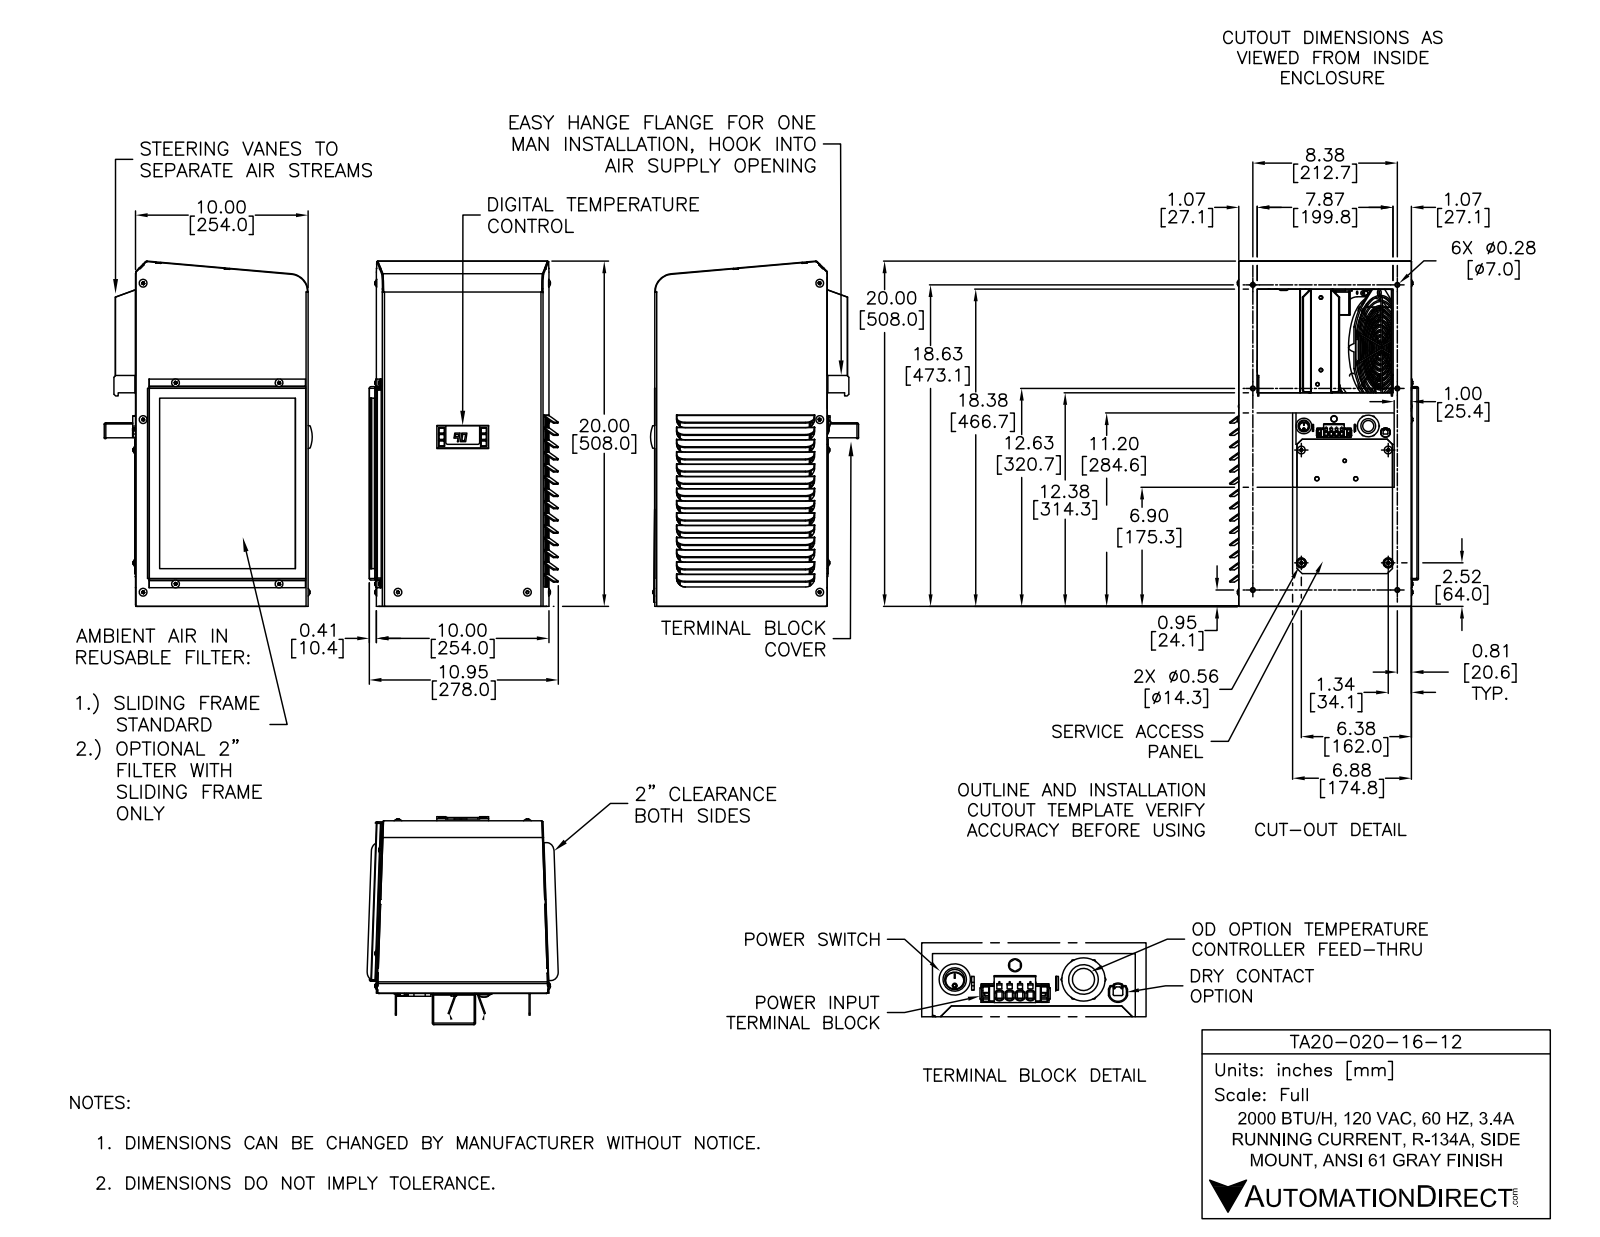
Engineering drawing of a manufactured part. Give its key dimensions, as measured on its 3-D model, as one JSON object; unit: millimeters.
{"part_name": "TA20-020-16-12", "step_written_by": "SolidWorks 2019 (AUTOMOTIVE_DESIGN)", "units": "millimeters", "bodies": {"solids": 52, "faces": 2157, "planar": 1121, "cylindrical": 737, "other": 299}, "overall_size": [508, 288.1, 279.5], "volume_mm3": 6576000, "surface_area_mm2": 1777000, "round_holes": [[5.2, 17], [5.1, 6], [8.7, 6], [1.1, 4], [3, 4], [3.6, 4], [4.2, 4], [5.6, 4], [2.3, 2], [3.2, 2], [4.2, 2], [6.4, 2]], "round_bosses_or_shafts": [[4.8, 16], [11.2, 6], [9.1, 2], [2.7, 2], [25.4, 1], [23, 1], [22, 1], [21.1, 1]], "partial_cylinders_radius": [[0.4, 100], [0.3, 96], [0.8, 44], [0.8, 33], [2.5, 22], [0.3, 16], [2.3, 14], [2.3, 13]], "face_to_face_distances": [1.5, 1.5, 254, 252.5, 252.5, 251, 4.7, 6.2, 66.6, 71.3], "hole_center_spacings": [5.1, 10.2, 152.4, 152.4, 295.9, 332.8, 209.6, 212.7]}
